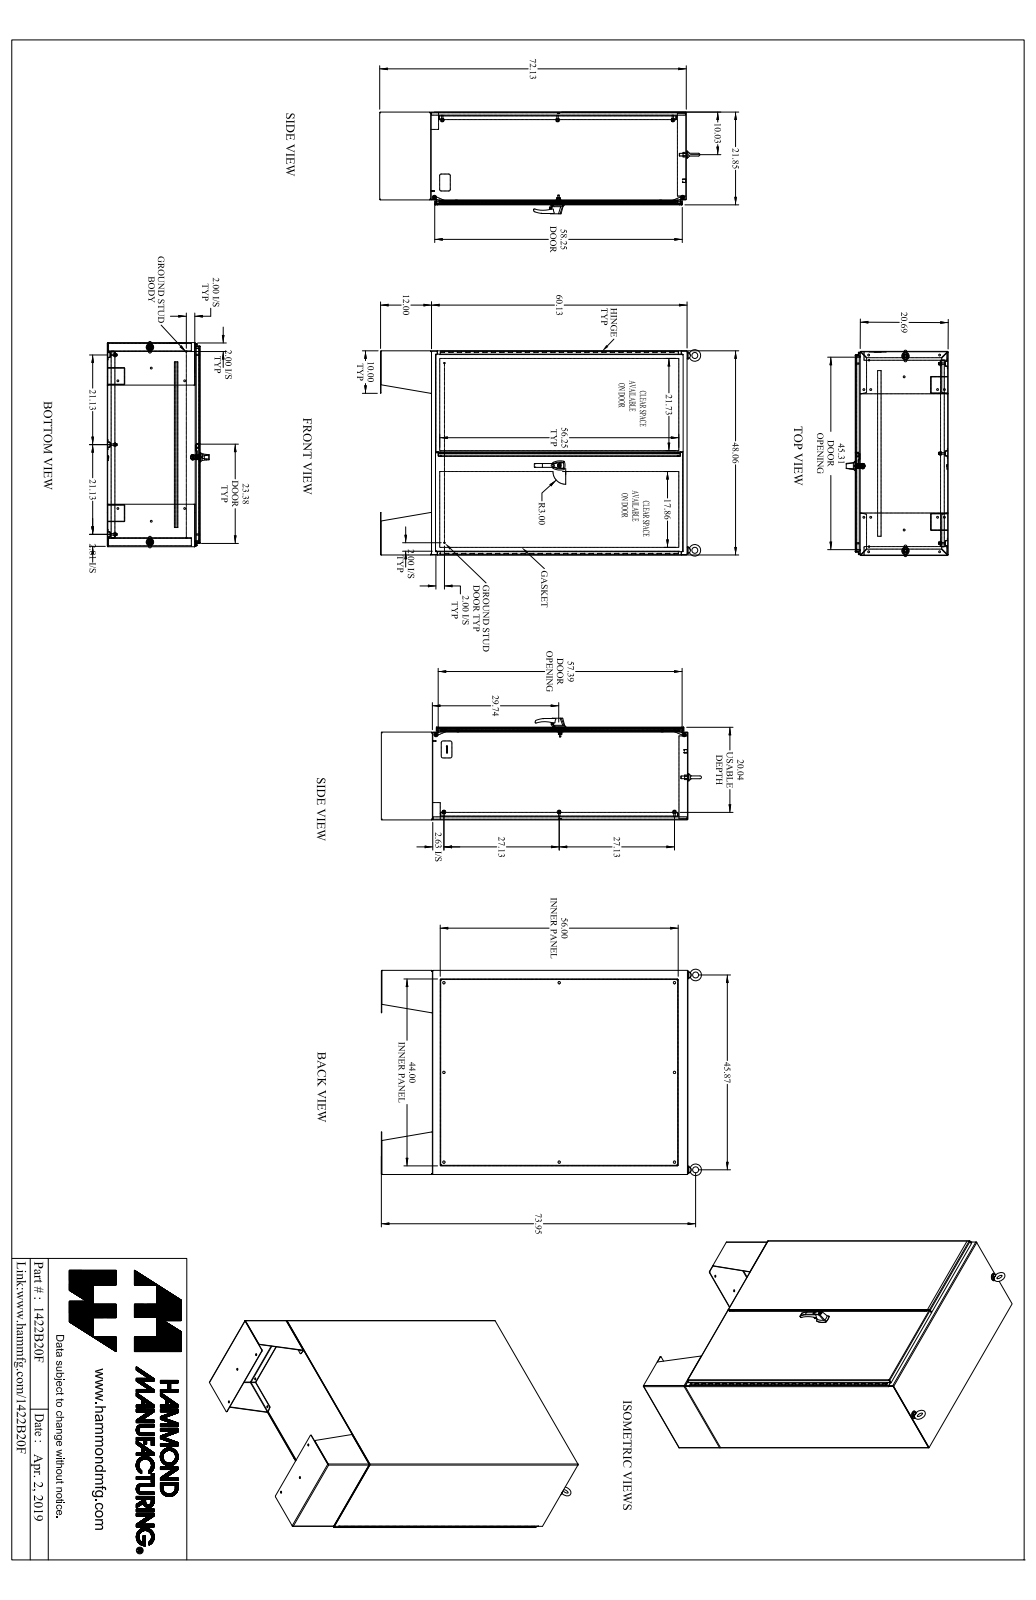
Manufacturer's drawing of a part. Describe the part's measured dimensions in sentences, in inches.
The part is named "1422B20F_Default". Its 3-D file was written by "SolidWorks 2019 (CONFIG_CONTROL_DESIGN)". It is 90 solids with 2769 faces: 1280 planar, 1242 cylindrical and 247 other. Overall it measures 75.778 by 49.121 by 23.963 inches. Its volume is 1 650 cubic inches and its surface area 33 052 square inches. Round holes: 20 of diameter 0.304, 14 of diameter 0.437, 9 of diameter 0.307, 8 of diameter 0.563, 6 of diameter 0.445, 2 of diameter 0.11, 2 of diameter 0.25, 2 of diameter 0.257, 2 of diameter 0.28, 2 of diameter 0.281, 2 of diameter 0.313, 2 of diameter 0.39. Round bosses or shafts: 10 of diameter 1, 8 of diameter 0.65, 8 of diameter 0.375, 8 of diameter 0.33, 6 of diameter 0.281, 4 of diameter 0.25, 2 of diameter 1.75, 2 of diameter 1.5. Partial cylindrical surfaces (rounded edges, fillets, slot ends): 32 of radius 0.048, 32 of radius 0.143, 22 of radius 0.125, 16 of radius 0.018, 14 of radius 0.06, 12 of radius 0.116, 8 of radius 0.05, 8 of radius 0.185. The main face-to-face distances are 0.095, 0.095, 47.968, 21.658, 21.753, 21.753, 21.848, 0.125, 20.066, 19.971. The hole center spacings are 6, 46.778, 12, 47.919, 18, 49.762, 24, 52.232.
